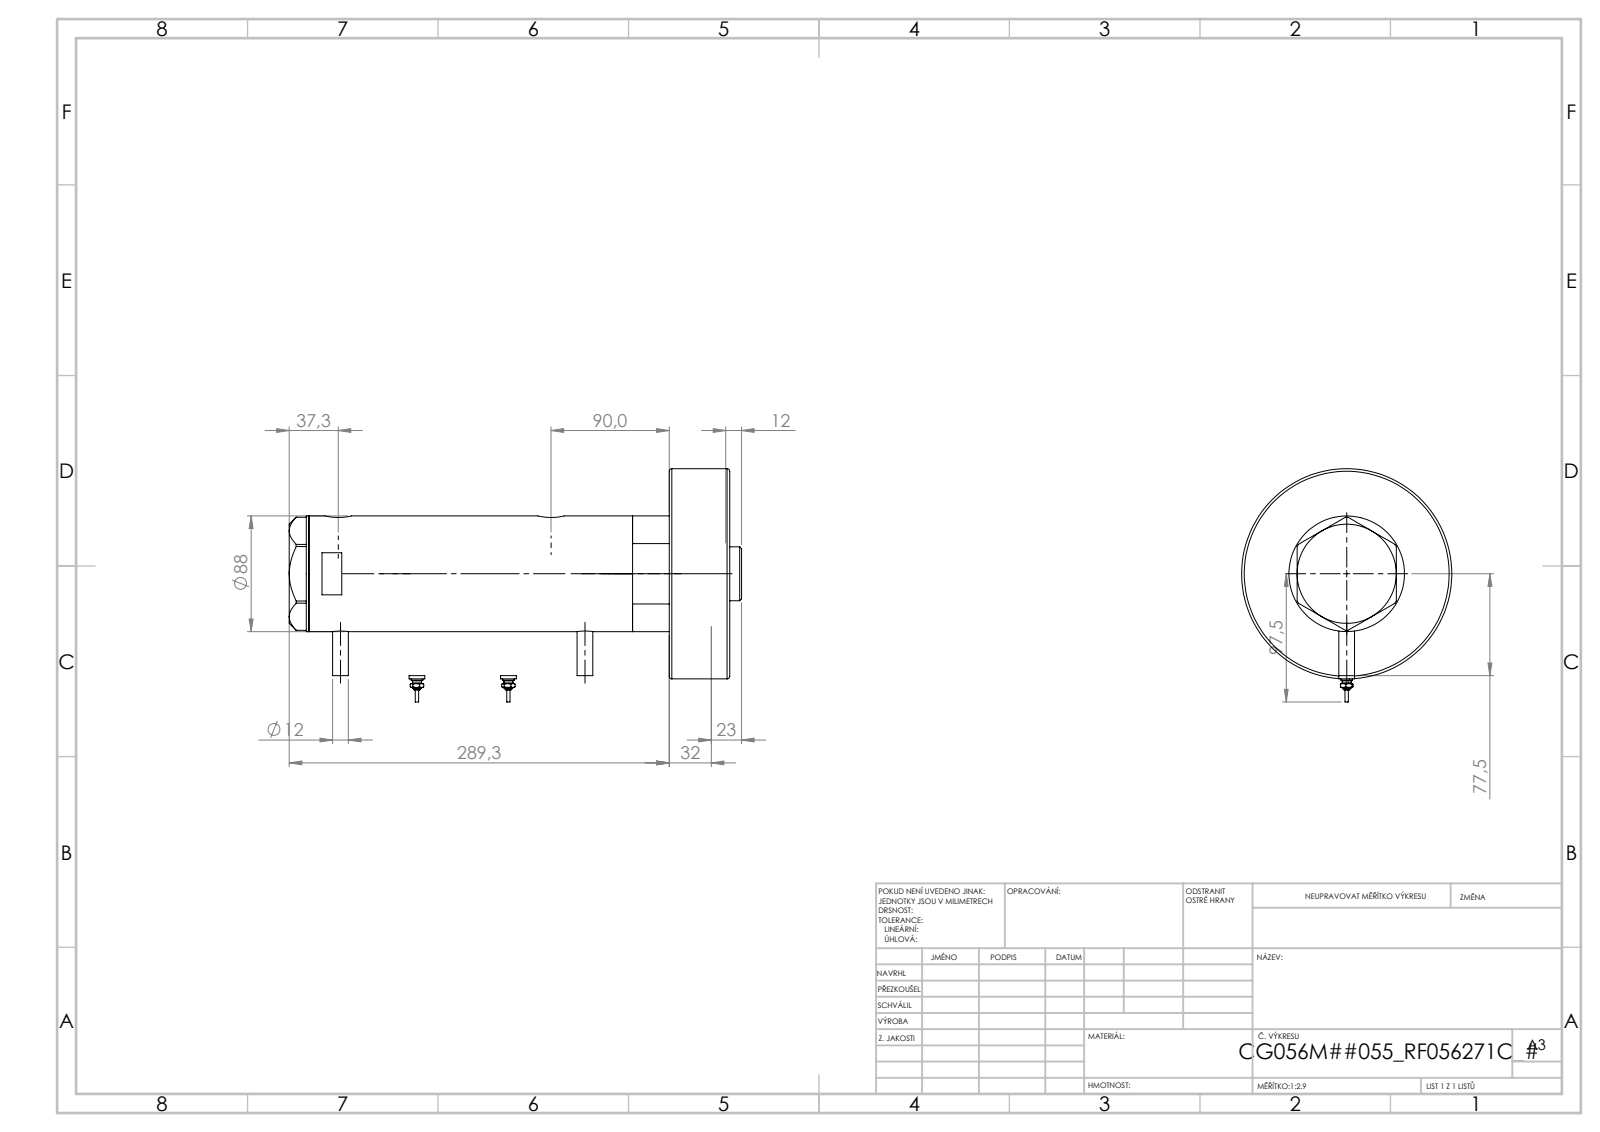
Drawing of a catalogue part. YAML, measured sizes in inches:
part_name: "V270CG_271C; V270CG_MIDDLE; V270CG_SWITCH; V270CG_BACK (+2 more)"
step_written_by: "SolidWorks 2019 (CONFIG_CONTROL_DESIGN)"
units: inches
bodies: {solids: 7, faces: 242, planar: 83, cylindrical: 81, other: 78}
overall_size: [11.003, 6.299, 6.299]
volume: 131.9
surface_area: 432.2
round_holes:
  - {diameter: 0.197, count: 2}
  - {diameter: 0.492, count: 2}
  - {diameter: 0.518, count: 2}
  - {diameter: 0.787, count: 2}
  - {diameter: 0.571, count: 1}
  - {diameter: 1.654, count: 1}
  - {diameter: 1.713, count: 1}
  - {diameter: 2.205, count: 1}
  - {diameter: 2.362, count: 1}
  - {diameter: 2.953, count: 1}
  - {diameter: 3.15, count: 1}
round_bosses_or_shafts:
  - {diameter: 0.472, count: 2}
  - {diameter: 0.354, count: 2}
  - {diameter: 0.276, count: 2}
  - {diameter: 0.171, count: 2}
  - {diameter: 0.094, count: 2}
  - {diameter: 6.299, count: 1}
  - {diameter: 3.465, count: 1}
  - {diameter: 2.874, count: 1}
face_to_face_distances: [1.811, 8.146, 9.957, 5.094, 3.051, 4.862, 1.024, 4.071, 7.122, 8.933]
hole_center_spacings: [0.067, 1.016, 4.146, 4.213, 5.161, 5.228]
